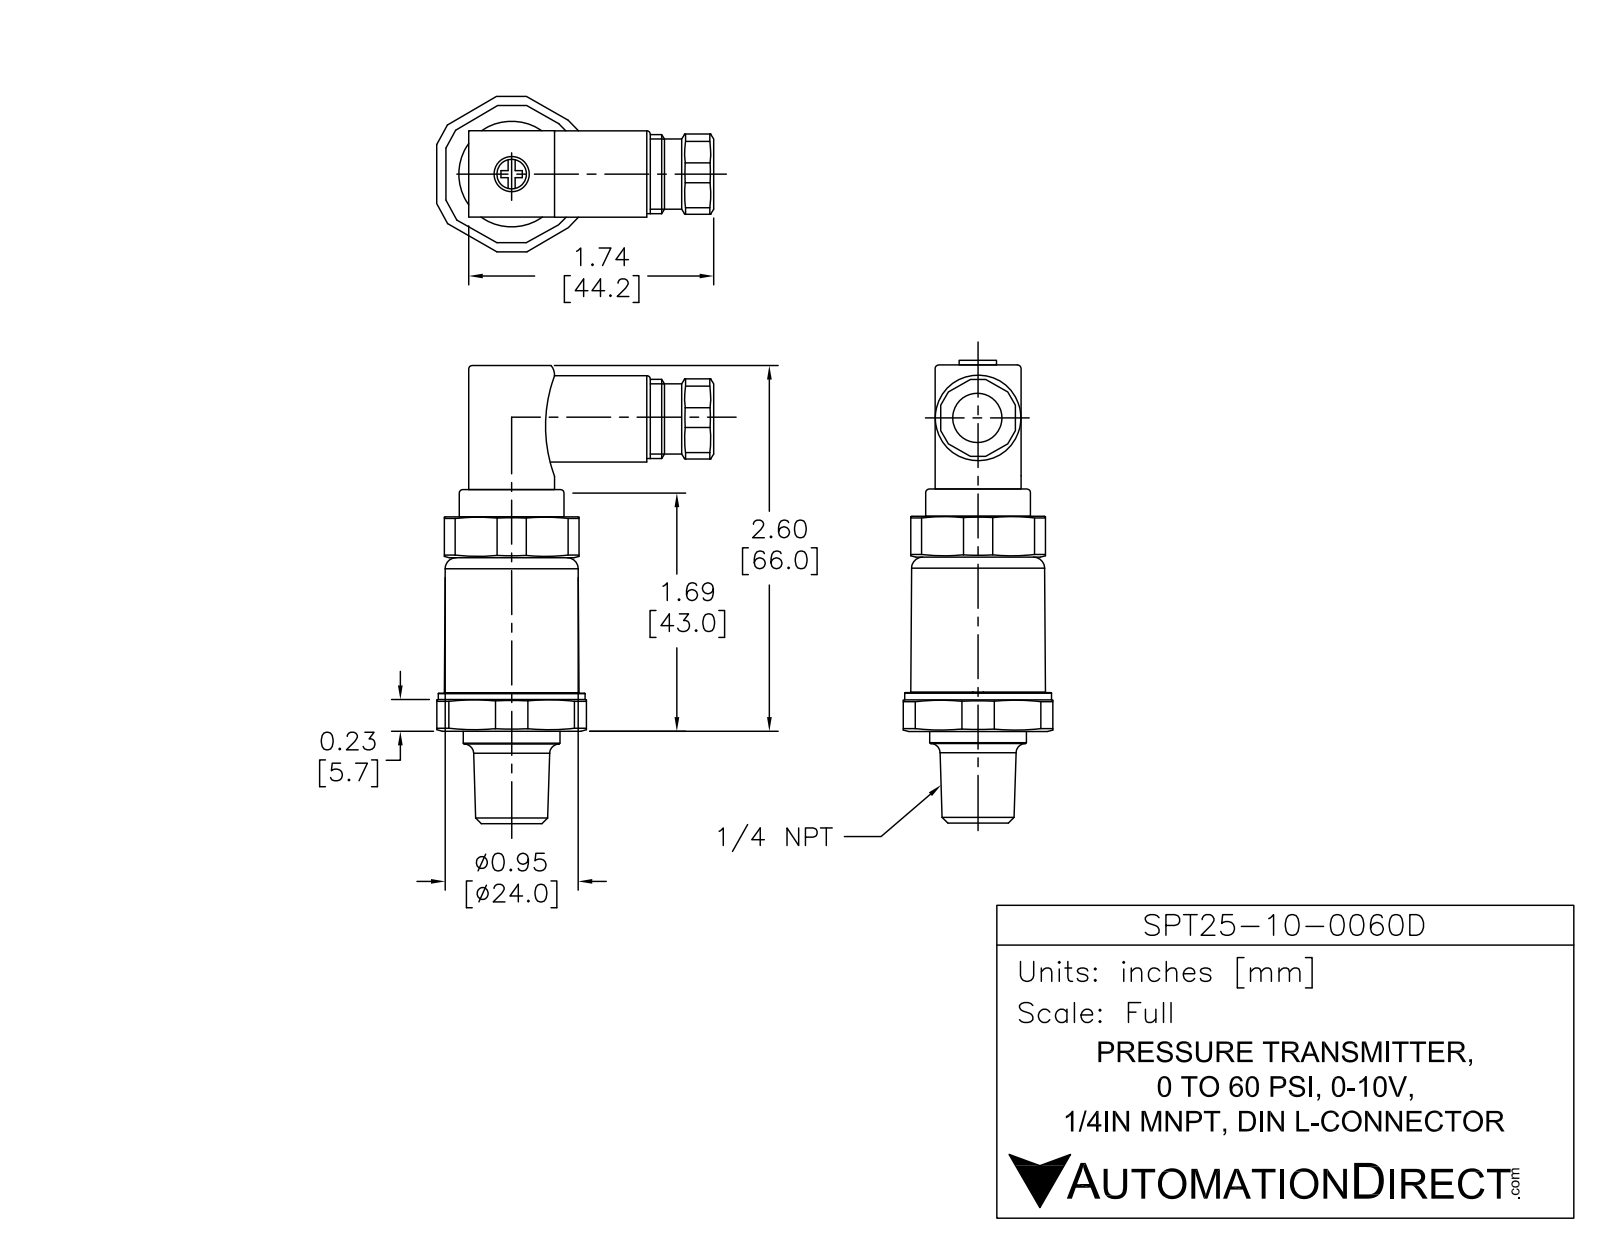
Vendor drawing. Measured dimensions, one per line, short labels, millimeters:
name: SPT25-10-0060D
written by: SolidWorks 2011 (AUTOMOTIVE_DESIGN)
unit: mm
bodies: 5 solids, 170 faces (96 planar, 64 cylindrical, 10 other)
size: 81.25 × 38.01 × 35.71
volume: 27 900 mm³; area: 10 134 mm²
holes: 1× ⌀1, 1× ⌀3.3, 1× ⌀7, 1× ⌀8
bosses: 1× ⌀26.75, 1× ⌀24, 1× ⌀17.5, 1× ⌀15, 1× ⌀14, 1× ⌀11
rounds: 8× R1.5, 4× R1.15, 4× R2.25, 3× R2, 1× R1.15, 1× R1.17, 1× R14.5
face distances: 1.5, 29.5, 31, 15.75, 0.35, 15.4, 6.75, 37.75, 36.25, 5
hole spacings: 1.33
